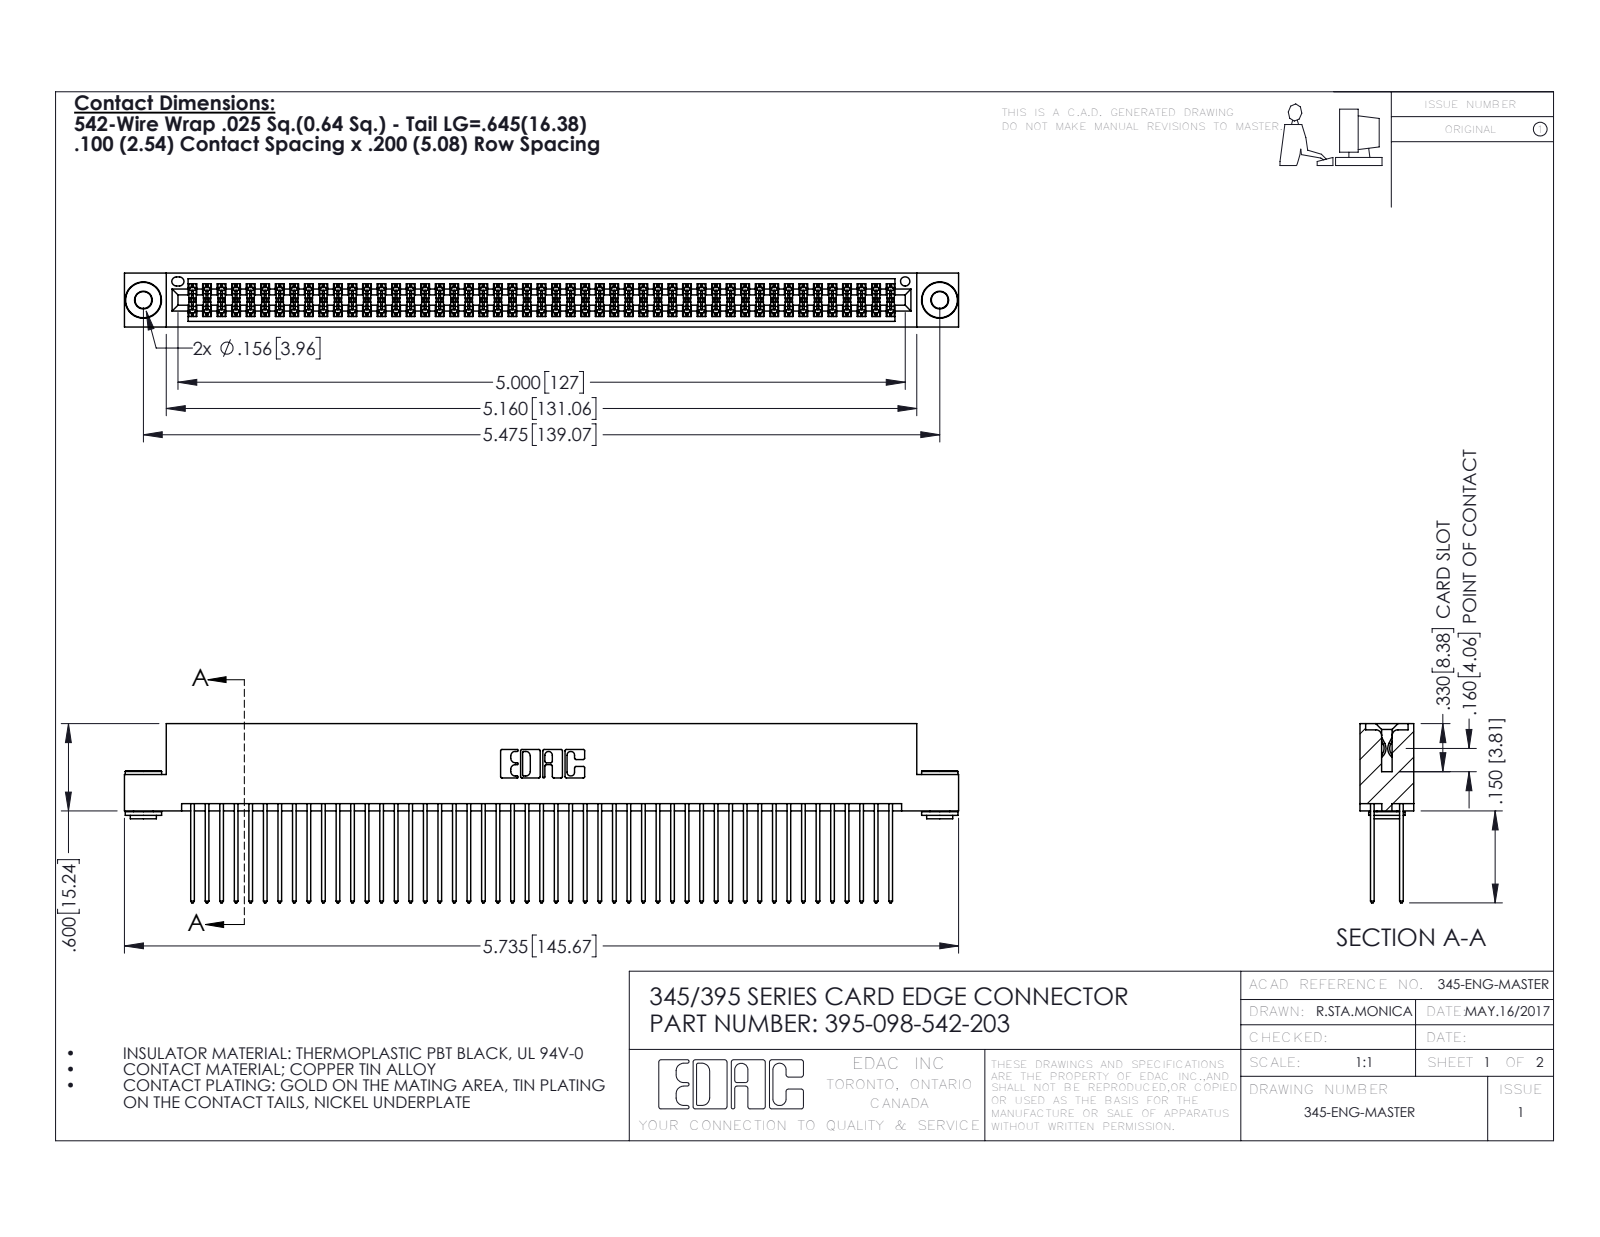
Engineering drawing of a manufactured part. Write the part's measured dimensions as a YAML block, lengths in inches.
part_name: "345-250-002_345-250-002-102; 345-292-001_345-293-142; 345 Part_Flush Mounting Lugs - 0.156 Dia-TH; 395-098-542-203"
step_written_by: "SolidWorks 2016 (CONFIG_CONTROL_DESIGN)"
units: inches
bodies: {solids: 101, faces: 5064, planar: 3324, cylindrical: 1732, other: 8}
overall_size: [5.735, 1.232, 0.37]
volume: 0.897
surface_area: 37.5
round_holes:
  - {diameter: 0.116, count: 2}
  - {diameter: 0.156, count: 2}
  - {diameter: 0.064, count: 1}
round_bosses_or_shafts:
  - {diameter: 0.25, count: 2}
  - {diameter: 0.18, count: 2}
  - {diameter: 0.136, count: 2}
partial_cylinders:
  - {radius: 0.006, count: 147}
  - {radius: 0.01, count: 98}
  - {radius: 0.01, count: 22}
  - {radius: 0.007, count: 6}
  - {radius: 0.031, count: 6}
  - {radius: 0.026, count: 3}
  - {radius: 0.014, count: 2}
  - {radius: 0.019, count: 2}
face_to_face_distances: [0.072, 0.298, 0.2, 0.025, 0.098, 0.272, 0.225, 0.37, 0.175, 0.149]
hole_center_spacings: [0.27, 5.239, 5.475]
